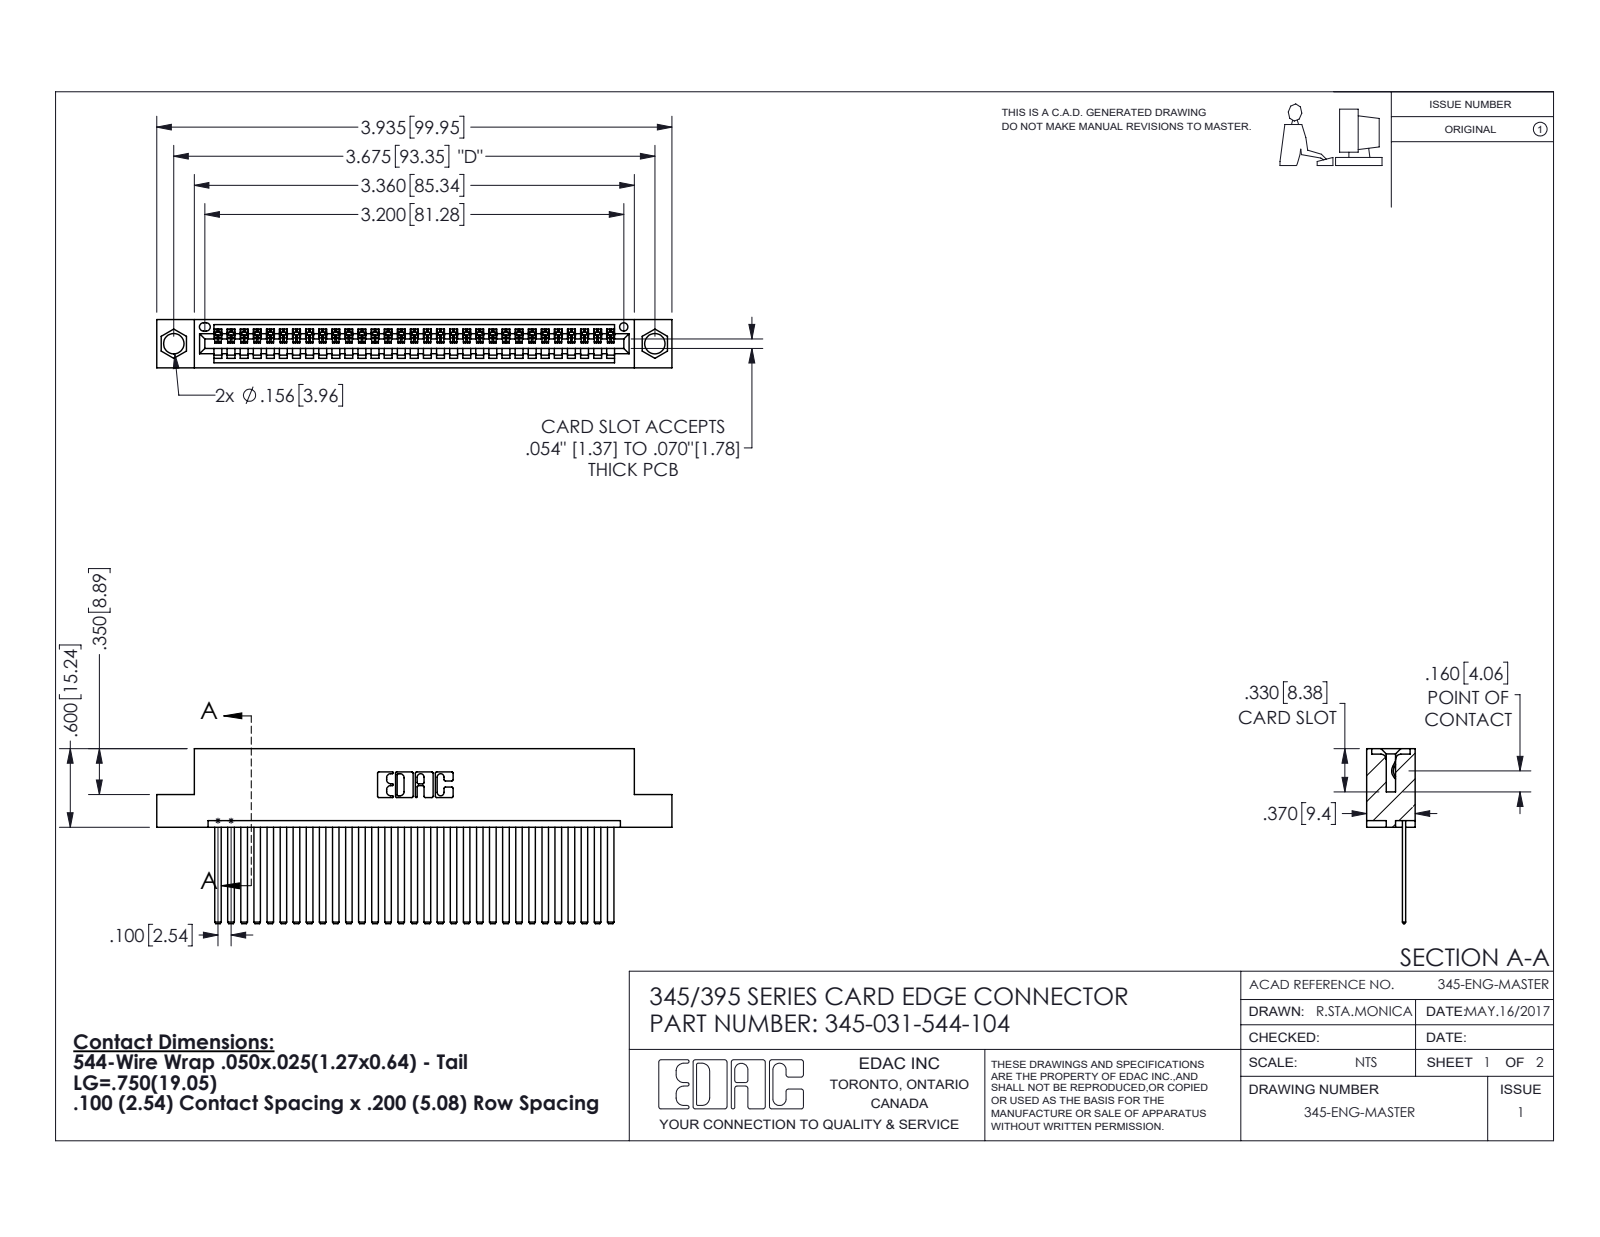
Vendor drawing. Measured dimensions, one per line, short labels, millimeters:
name: 345-031-544-104; 345-292-001_345-293-144; 345 Part_Flush Mounting Lugs - 0.156 Dia-TH
written by: SolidWorks 2016 (CONFIG_CONTROL_DESIGN)
unit: mm
bodies: 32 solids, 1738 faces (1196 planar, 542 cylindrical, 0 other)
size: 99.9 × 34 × 9.4
volume: 9 670 mm³; area: 13 590 mm²
holes: 2× ⌀4, 1× ⌀1.6
rounds: 62× R0.2, 22× R0.3, 6× R0.2, 6× R0.8, 3× R0.7, 2× R0.8, 2× R1, 1× R0.4
face distances: 1.8, 7.6, 2.5, 0.6, 6.9, 5.1, 9.4, 5.7, 3.8, 1.8
hole spacings: 6.9, 87.4, 93.3
